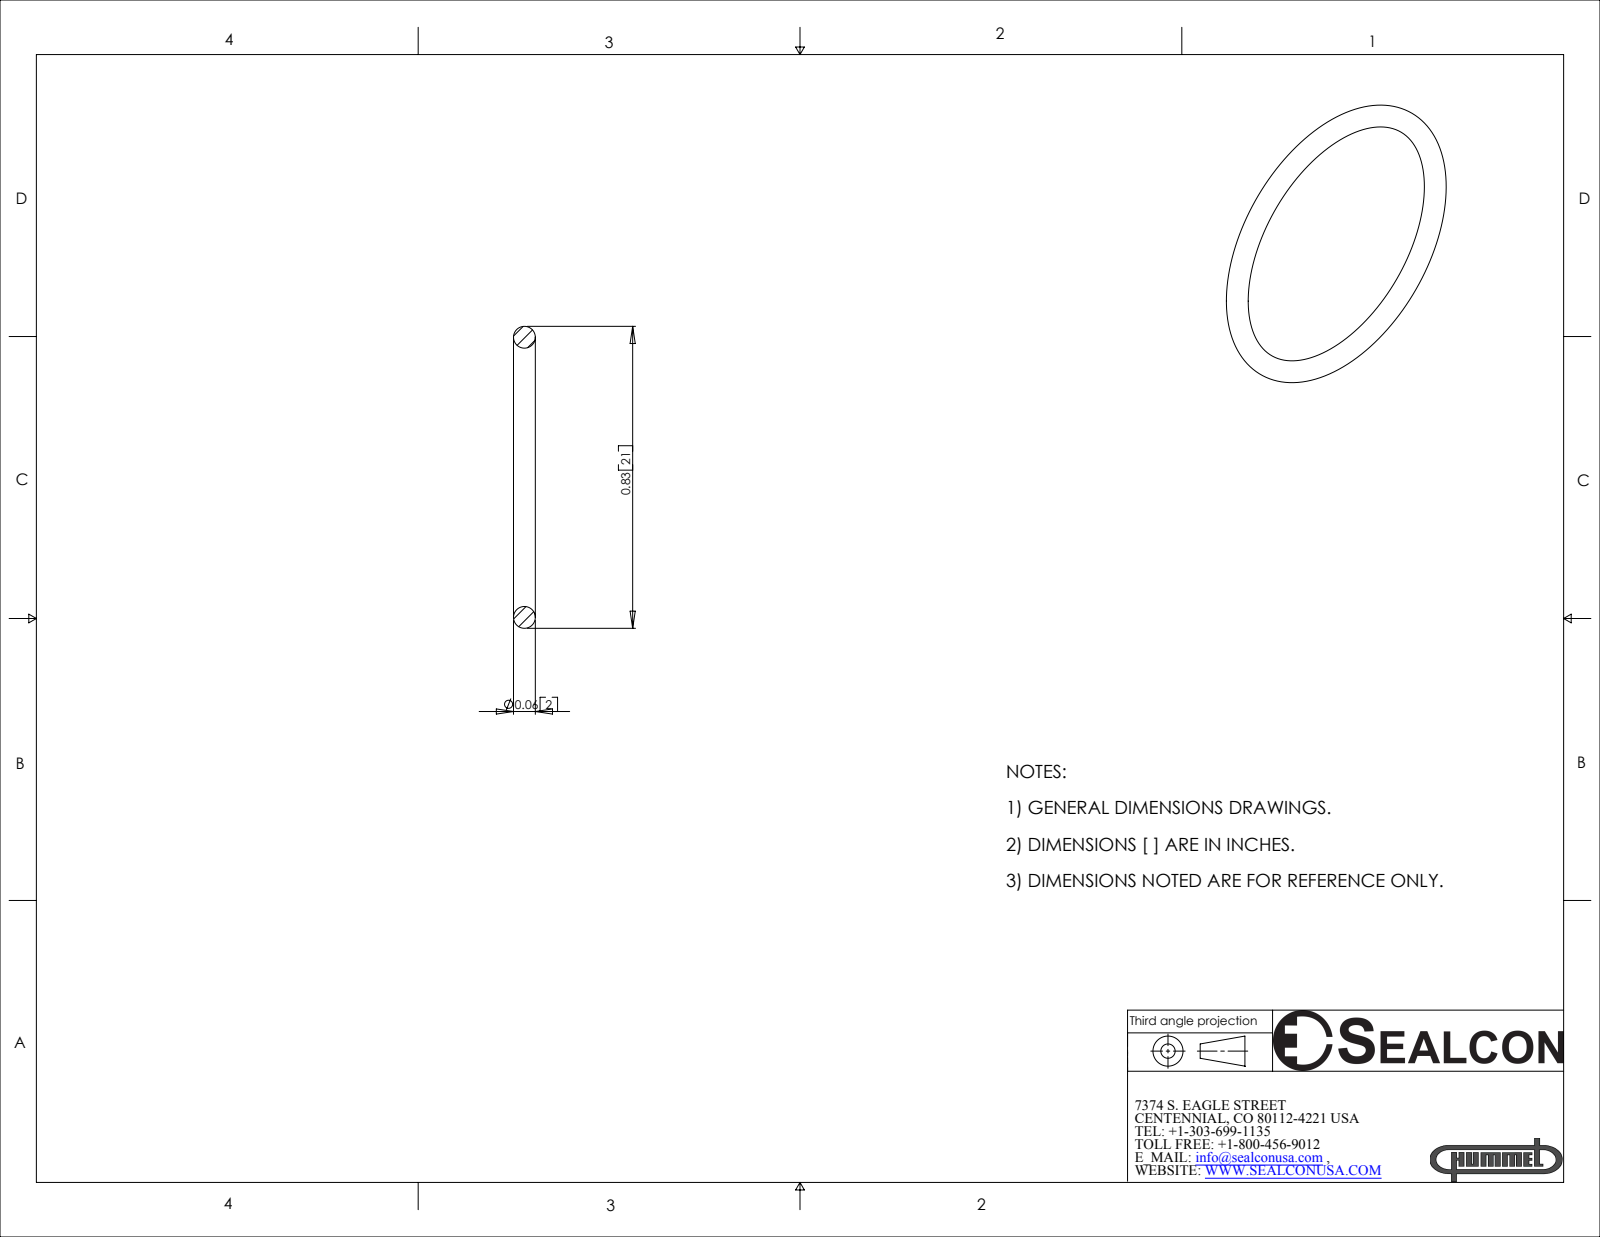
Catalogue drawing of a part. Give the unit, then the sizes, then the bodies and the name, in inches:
Units: inches
Overall size (bounding box): 0.83 × 0.83 × 0.06
Volume: 0.007 in³ · Surface area: 0.456 in²
Bodies: 1 solid, 4 faces (0 planar, 0 cylindrical, 4 other)
Part name (STEP PRODUCT): OR-16-VT
STEP written by: SolidWorks 2007 (CONFIG_CONTROL_DESIGN)
